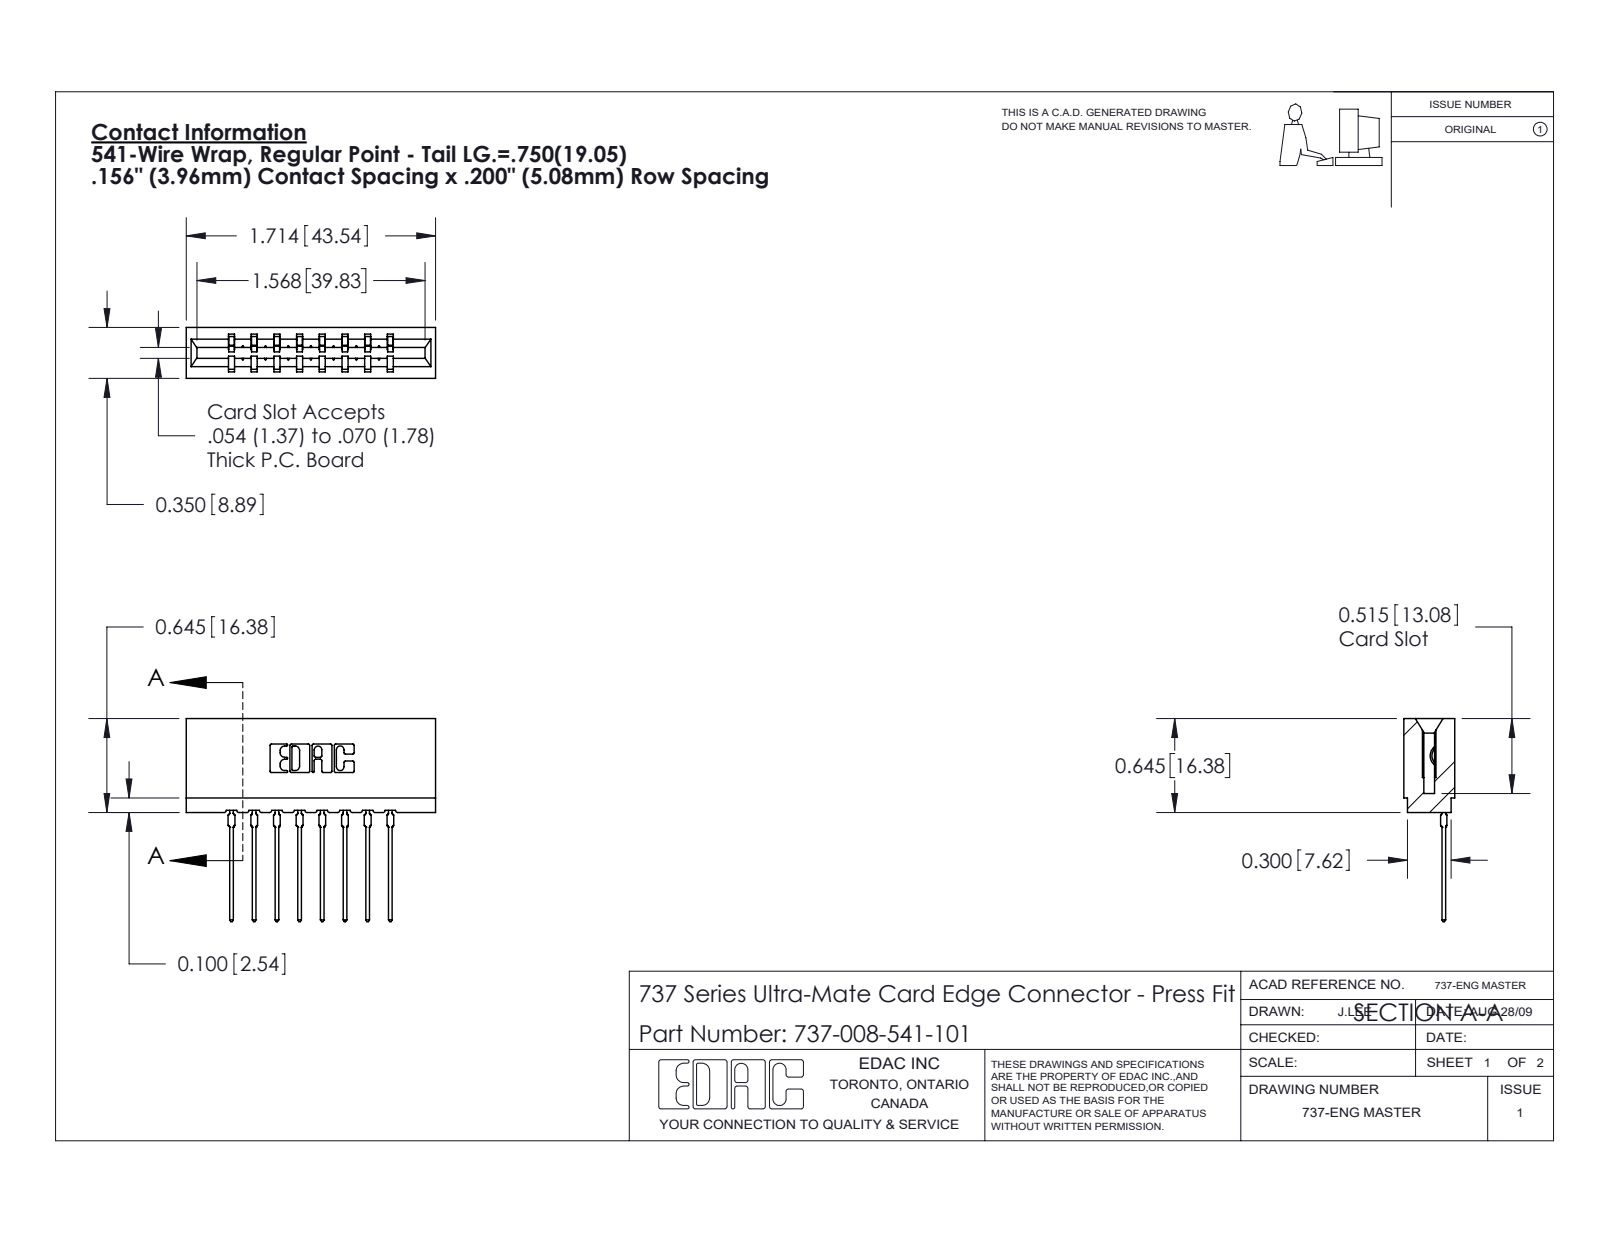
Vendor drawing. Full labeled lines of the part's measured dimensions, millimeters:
Part name (STEP PRODUCT): 737-008-541-101; 745-292-001_541; 737 Part_Insulator Option - 01
STEP written by: SolidWorks 2020 (CONFIG_CONTROL_DESIGN)
Units: millimetres
Bodies: 9 solids, 998 faces (598 planar, 192 cylindrical, 208 other)
Overall size (bounding box): 43.5 × 35.5 × 8.9
Volume: 4 470 mm³ · Surface area: 5 562 mm²
Partial cylindrical surfaces — rounded edges, fillets, slot ends (radius × count): R0.3 ×22, R0.4 ×16, R0.5 ×16, R0.2 ×6, R0.8 ×6, R0.1 ×4, R0.3 ×4, R0.7 ×3
Main face-to-face distances: 4, 3.5, 5.4, 8.9, 15.8, 7.9, 9, 5, 11.9, 19.8
